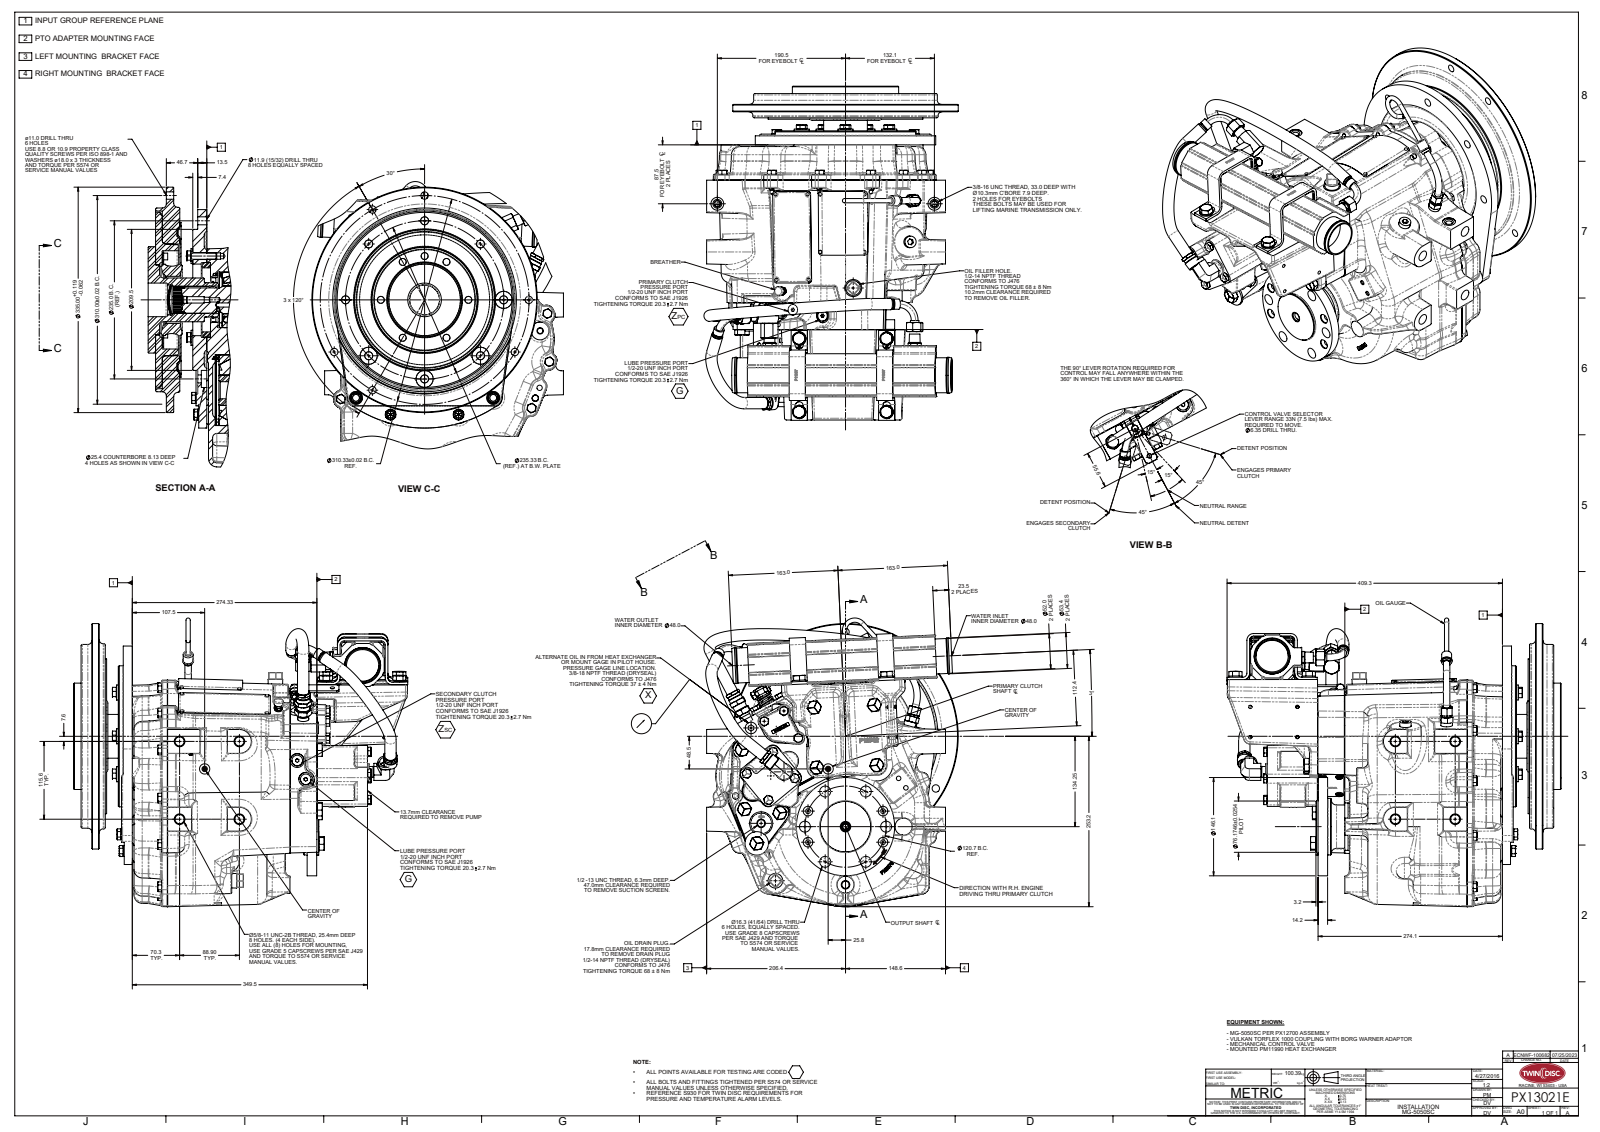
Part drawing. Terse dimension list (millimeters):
name: PX13021E
written by: SolidWorks 2019 (AUTOMOTIVE_DESIGN)
unit: mm
bodies: 0 solids, 3342 faces (915 planar, 858 cylindrical, 1569 other)
size: 496.5 × 429.07 × 377.92
holes: 7× ⌀7.94, 7× ⌀11.91, 6× ⌀11, 6× ⌀16.27, 4× ⌀5, 4× ⌀7.14, 4× ⌀14.29, 4× ⌀15.87, 4× ⌀19.05, 3× ⌀9.54, 3× ⌀10.32, 3× ⌀20.64
bosses: 6× ⌀18.87, 5× ⌀12.56, 4× ⌀19.85, 4× ⌀16.9, 4× ⌀16, 4× ⌀15.88, 3× ⌀14.14, 3× ⌀6.35
rounds: 67× R1.52, 63× R8.13, 32× R0.4, 27× R3, 24× R8, 24× R10.16, 18× R0.51, 15× R3.81
face distances: 16, 234.3, 27, 2.54, 62.7, 310.46, 76.16, 0.66, 234.96, 311.12
hole spacings: 89.91, 117.48, 155, 166.14, 51.46, 109.88, 168.52, 217.07
